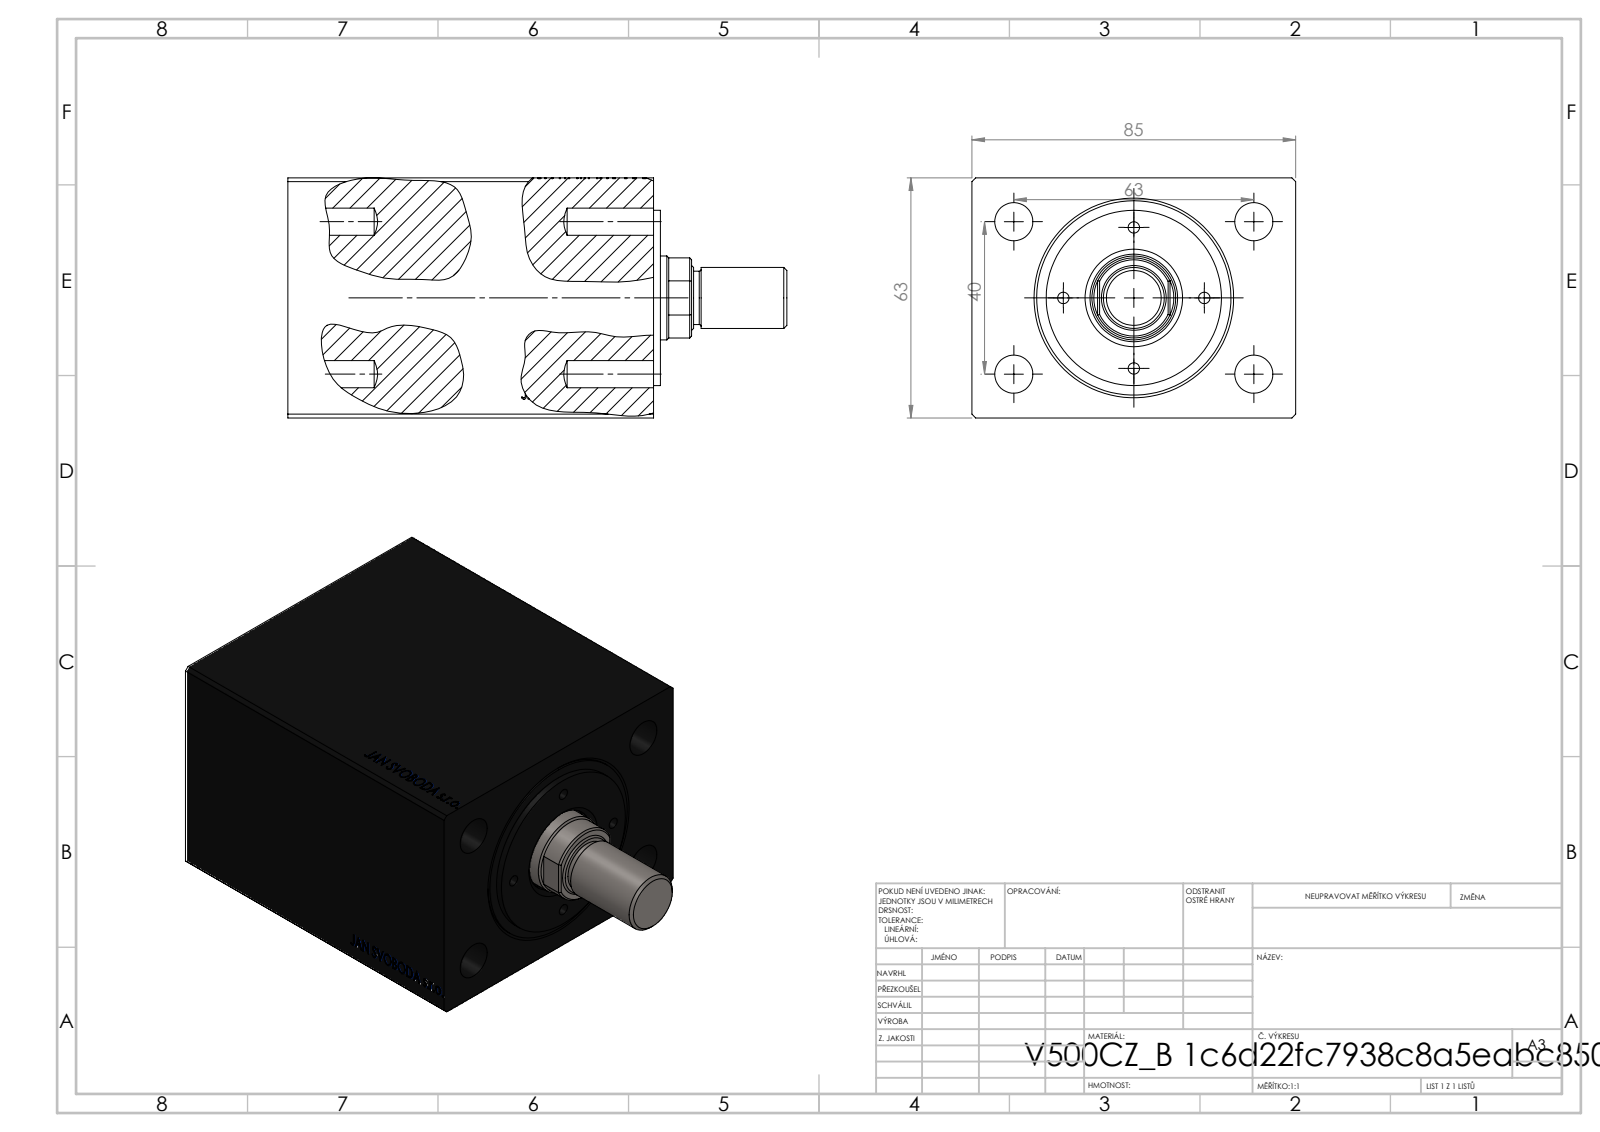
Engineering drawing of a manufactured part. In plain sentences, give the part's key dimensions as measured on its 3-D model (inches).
The part is named "V500CZ; V500CZ_MALE_METRIC; V500CZ_B_VC". Its 3-D file was written by "SolidWorks 2019 (CONFIG_CONTROL_DESIGN)". It is 4 solids with 887 faces: 403 planar, 62 cylindrical and 422 other. Overall it measures 5.157 by 3.346 by 2.48 inches. Its volume is 31.52 cubic inches and its surface area 143.1 square inches. Round holes: 4 of diameter 0.118, 4 of diameter 0.394, 2 of diameter 0.217, 2 of diameter 0.518, 2 of diameter 0.787, 1 of diameter 0.571, 1 of diameter 0.866, 1 of diameter 0.906, 1 of diameter 1.417, 1 of diameter 1.575, 1 of diameter 2.008. Round bosses or shafts: 1 of diameter 1.811, 1 of diameter 0.63, 1 of diameter 0.551. Partial cylindrical surfaces (rounded edges, fillets, slot ends): 1 of radius 0.413. The main face-to-face distances are 2.48, 3.346, 3.78, 0.984, 3.201, 0.579, 2.795, 0.406, 0.071, 2.866. The hole center spacings are 0.728, 0.939, 1.03, 1.242, 1.469, 1.958, 2.12, 1.457.
